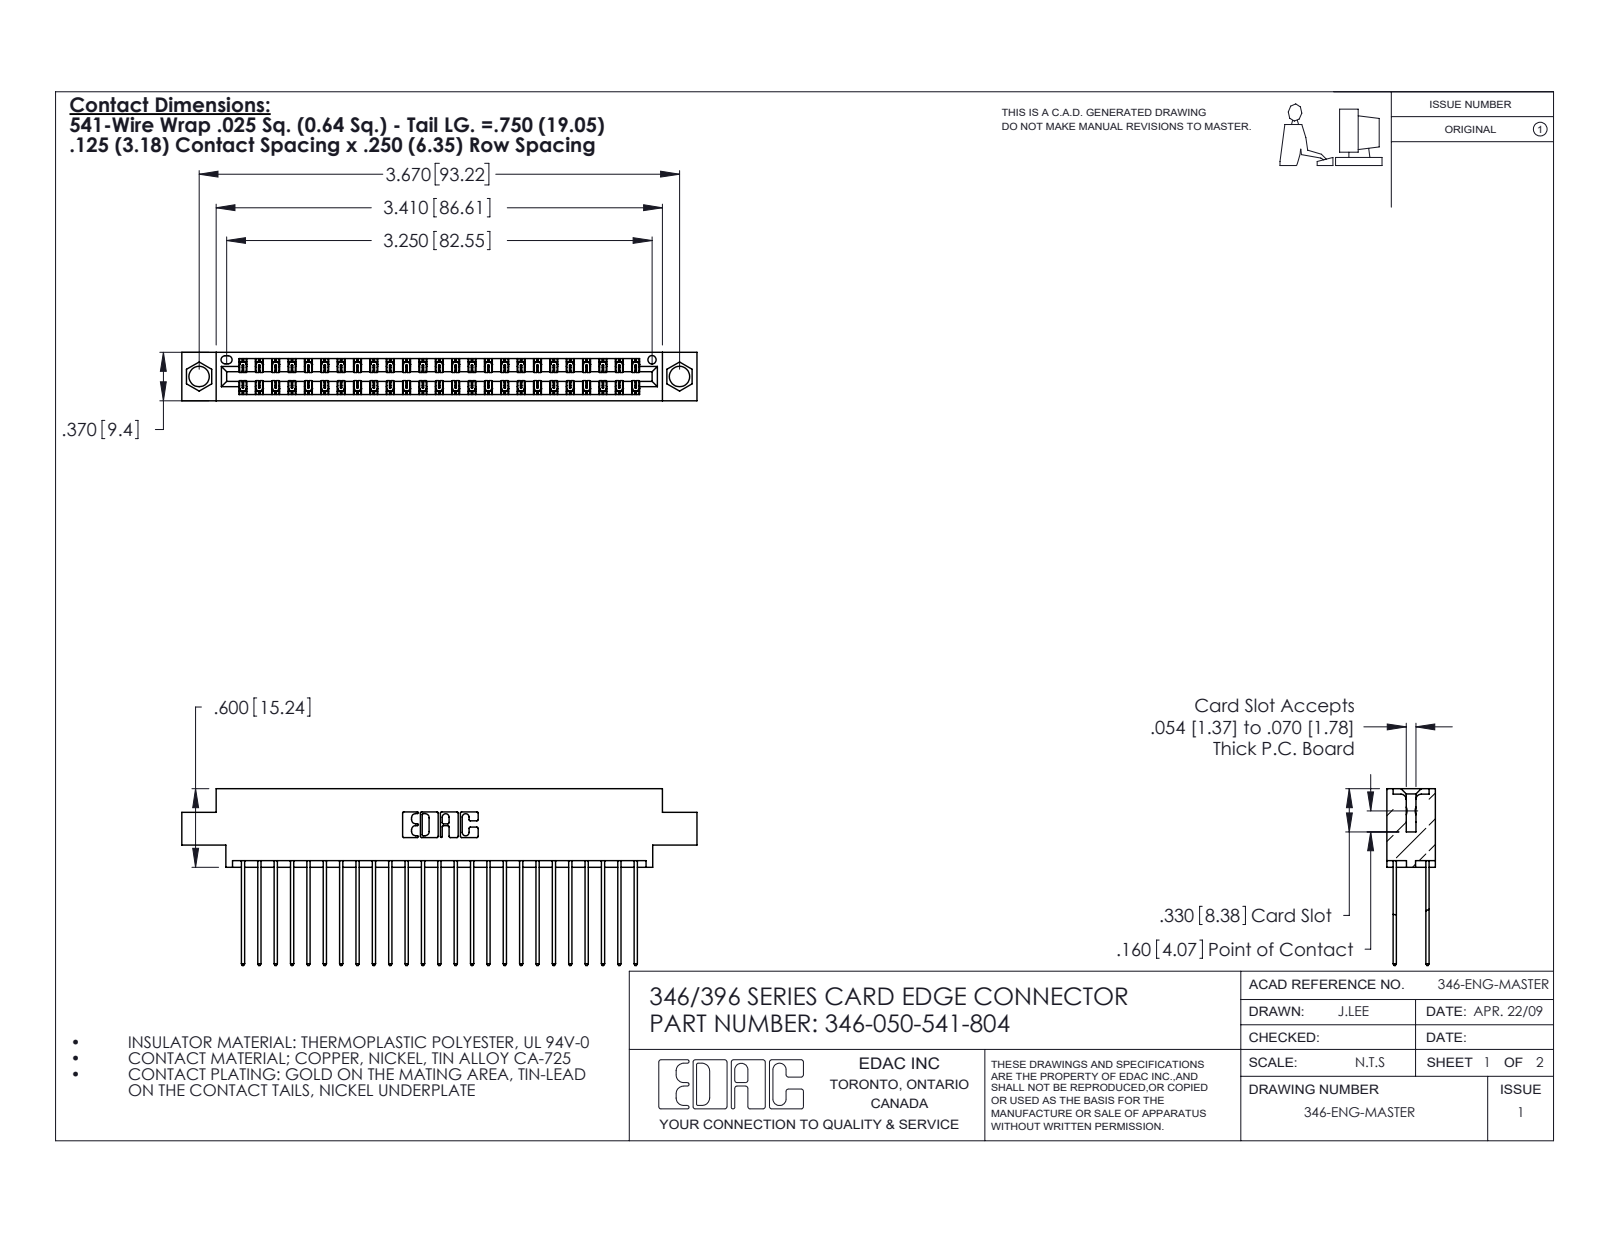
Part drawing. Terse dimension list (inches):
name: 346 Part_0.170 Offset - 0.156 Dia-TH; 345-292-001_345-293-141; 346-050-541-804
written by: SolidWorks 2020 (CONFIG_CONTROL_DESIGN)
unit: in
bodies: 51 solids, 2740 faces (1844 planar, 896 cylindrical, 0 other)
size: 3.935 × 1.35 × 0.37
volume: 0.588 in³; area: 22.3 in²
holes: 2× ⌀0.156, 1× ⌀0.064
rounds: 75× R0.006, 50× R0.01, 22× R0.01, 6× R0.007, 6× R0.031, 3× R0.026, 2× R0.014, 2× R0.022
face distances: 0.048, 0.322, 0.25, 0.072, 0.298, 0.025, 0.37, 0.275, 0.225, 0.222
hole spacings: 0.246, 3.462, 3.67
